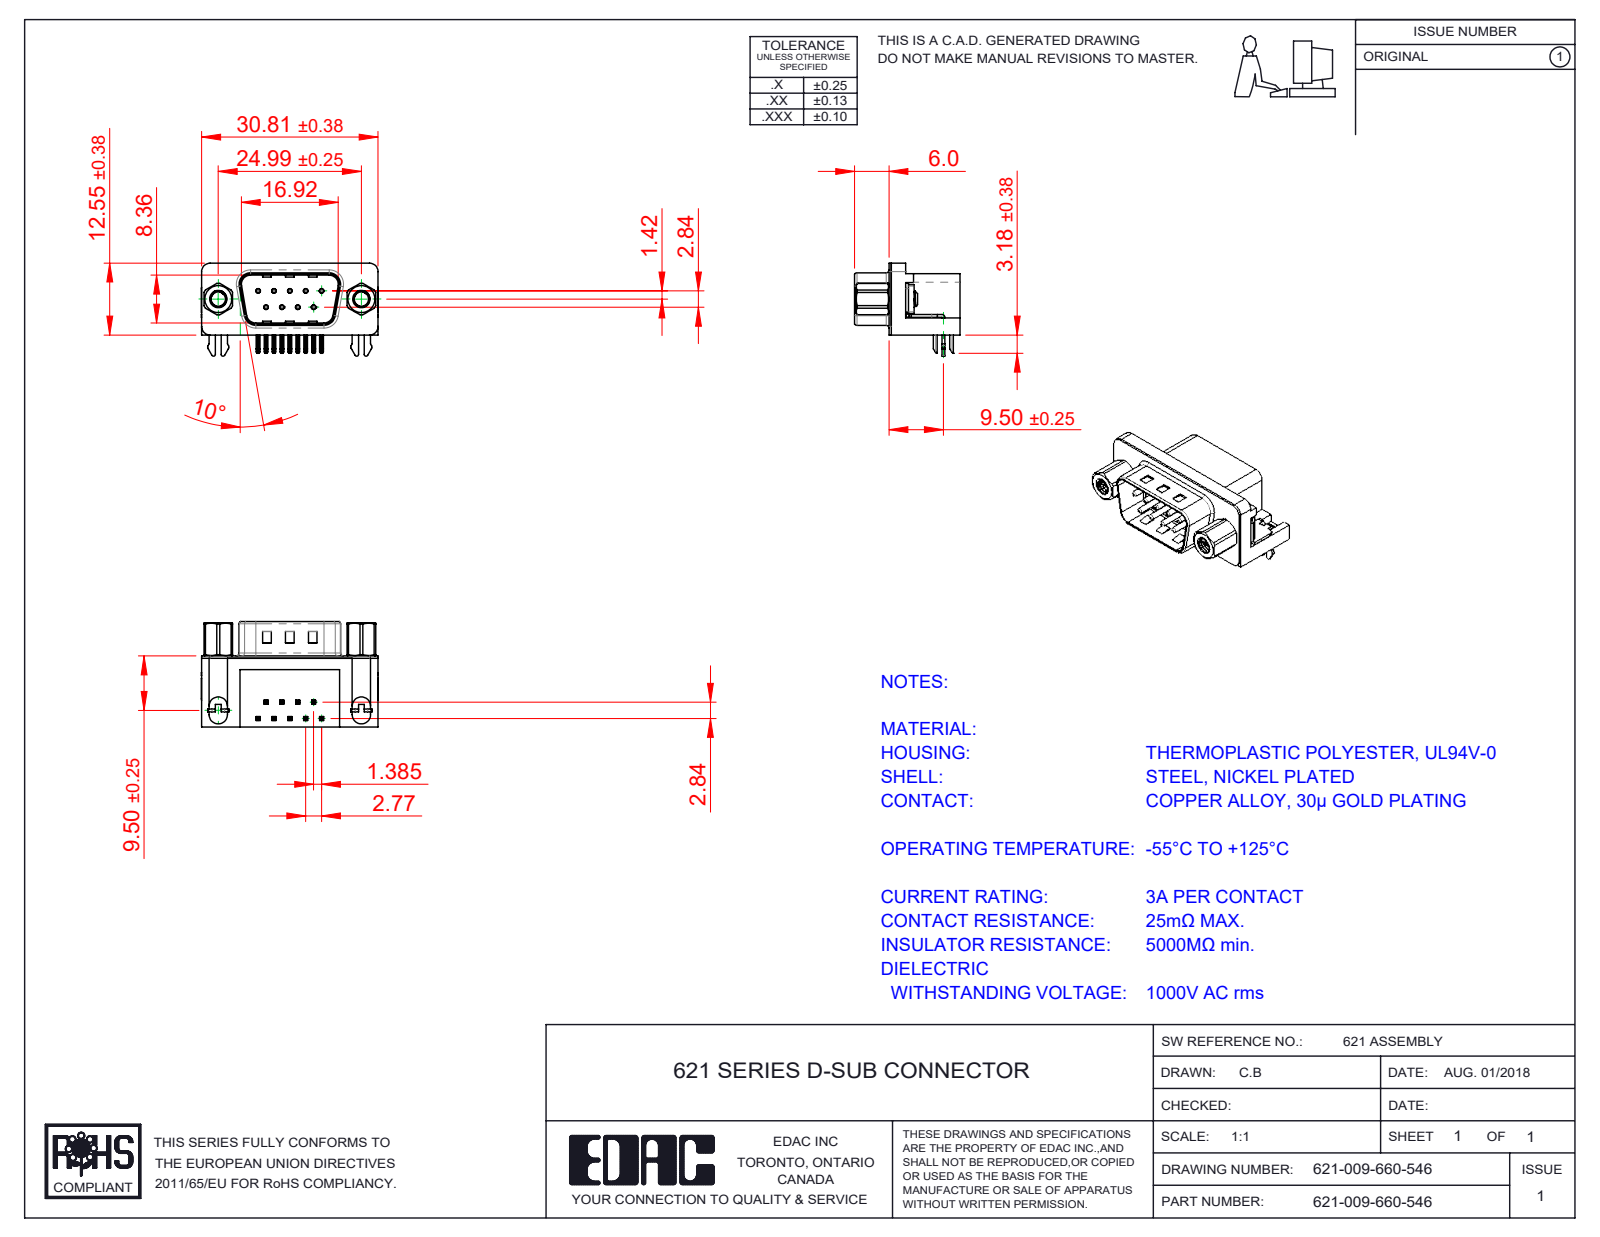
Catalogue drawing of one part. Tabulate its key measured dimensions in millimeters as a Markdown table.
| quantity | value |
| --- | --- |
| part name | 621 Housing_9 Socket; 621 M3 Hex Standoff 5; 621 Contact Top; 621 Contact Bottom (+4 more) |
| STEP written by | SolidWorks 2016 (CONFIG_CONTROL_DESIGN) |
| units | millimeters |
| bodies | 17 solids, 1259 faces (637 planar, 417 cylindrical, 205 other) |
| overall size | 30.89 × 18.4 × 16.25 |
| volume | 3 495 mm³ |
| surface area | 5 028 mm² |
| round holes (diameter × count) | 0.35 × 9, 0.8 × 9, 2 × 2, 2.5 × 2, 4 × 2, 4.8 × 2, 5 × 2 |
| round bosses / shafts (diameter × count) | 0.75 × 9, 3 × 4, 4.9 × 2, 4.75 × 2, 3.9 × 2 |
| partial cylindrical surfaces (radius × count) | 0.25 × 48, 0.12 × 18, 1 × 16, 0.5 × 9, 1.5 × 8, 1.6 × 8, 0.9 × 4, 2 × 4 |
| main face-to-face distances | 0.4, 12, 12.4, 10.35, 9.5, 2.5, 2.9, 2.1, 0.35, 10.7 |
| hole center spacings | 3.16, 2.77, 5.54, 5.03, 5.04, 8.31, 7.48, 7.49 |
